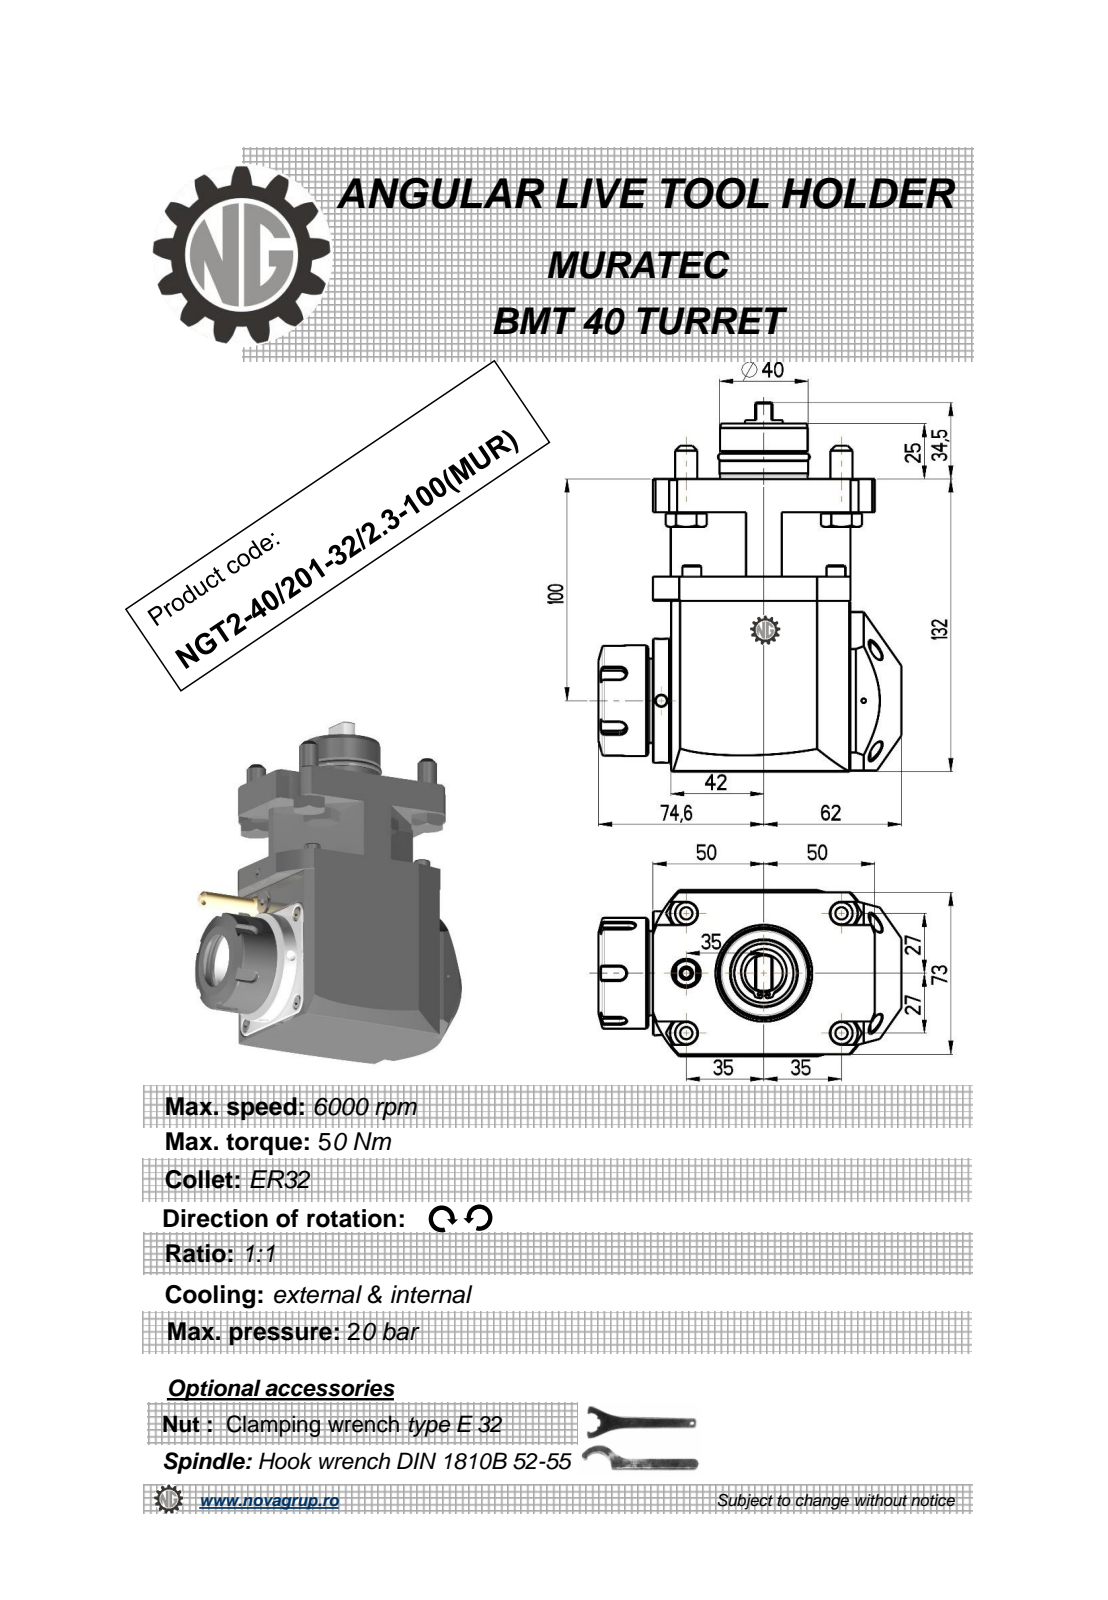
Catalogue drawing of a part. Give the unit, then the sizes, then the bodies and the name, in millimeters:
Units: millimetres
Overall size (bounding box): 166.5 × 136.6 × 75
Round holes (diameter × count): ⌀5 ×3, ⌀3 ×1, ⌀4.2 ×1, ⌀27 ×1
Round bosses / shafts (diameter × count): ⌀14.6 ×4, ⌀10 ×4, ⌀56 ×1, ⌀50 ×1, ⌀43 ×1, ⌀41 ×1, ⌀40 ×1, ⌀39.5 ×1
Partial cylindrical surfaces — rounded edges, fillets, slot ends (radius × count): R0.22 ×6, R3 ×5, R5.25 ×4, R6 ×1, R40 ×1, R53.5 ×1
Main face-to-face distances: 132, 75, 1, 74, 44, 88, 63, 15, 29, 117
Hole centre spacings: 11.25, 40.93
Volume: 912 310 mm³ · Surface area: 81 990 mm²
Bodies: 2 solids, 412 faces (177 planar, 84 cylindrical, 151 other)
Part name (STEP PRODUCT): NGT2_40_201_32_2_3_100_MUR
STEP written by: PRO/ENGINEER BY PARAMETRIC TECHNOLOGY CORPORATION, 2010280 (CONFIG_CONTROL_DESIGN)
